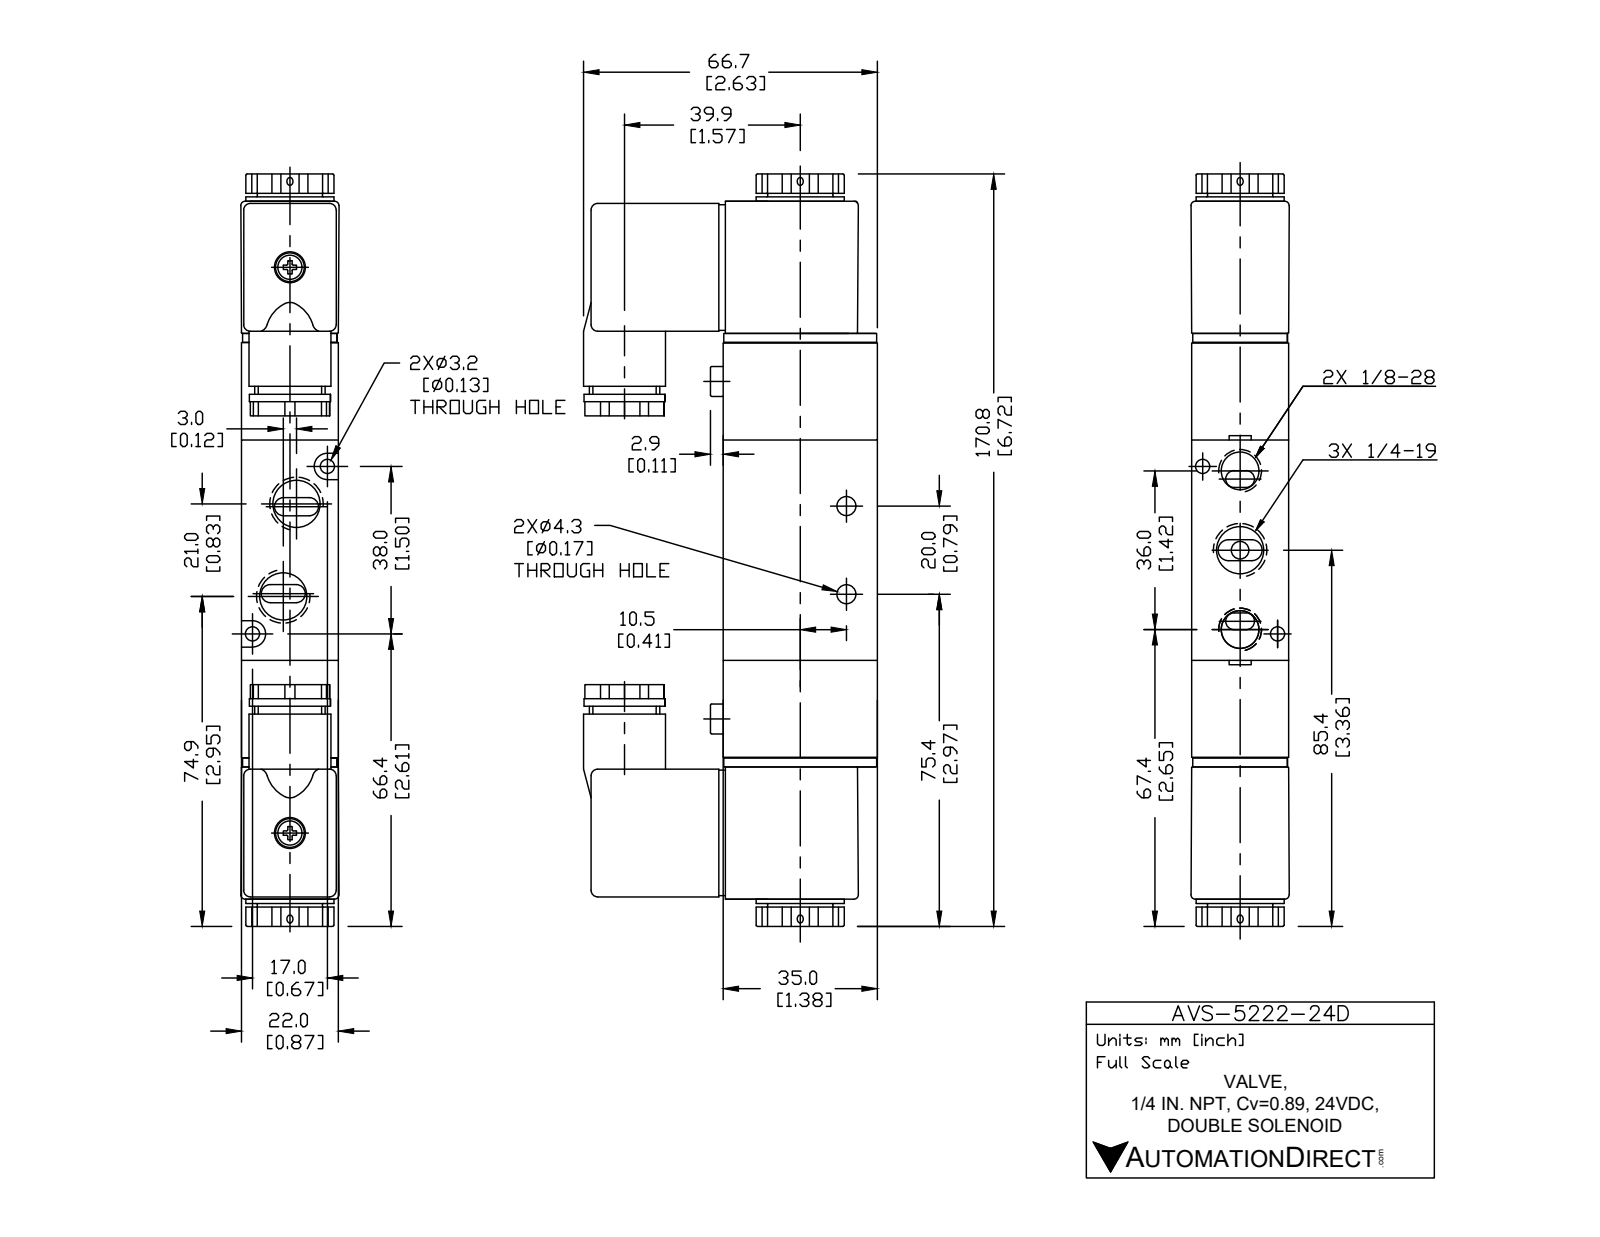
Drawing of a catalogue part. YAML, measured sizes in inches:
part_name: "AVS-5222-24D"
step_written_by: "SolidWorks 2015 (CONFIG_CONTROL_DESIGN)"
units: inches
bodies: {solids: 4, faces: 272, planar: 131, cylindrical: 109, other: 32}
overall_size: [6.724, 2.626, 0.866]
volume: 9.488
surface_area: 55.48
round_holes:
  - {diameter: 0.438, count: 3}
  - {diameter: 0.169, count: 2}
  - {diameter: 0.332, count: 2}
  - {diameter: 0.126, count: 1}
  - {diameter: 0.13, count: 1}
  - {diameter: 0.366, count: 1}
round_bosses_or_shafts:
  - {diameter: 0.787, count: 1}
  - {diameter: 0.732, count: 1}
  - {diameter: 0.724, count: 1}
  - {diameter: 0.63, count: 1}
  - {diameter: 0.583, count: 1}
  - {diameter: 0.264, count: 1}
partial_cylinders:
  - {radius: 0.059, count: 18}
  - {radius: 0.039, count: 10}
  - {radius: 0.061, count: 10}
  - {radius: 0.02, count: 8}
  - {radius: 0.118, count: 2}
face_to_face_distances: [0.02, 0.866, 0.846, 1.378, 0.901, 0.827, 1.969, 1.181, 2.559, 2.114]
hole_center_spacings: [0.337, 0.709, 0.819, 1.494, 0.297, 0.308, 0.415, 0.415]
